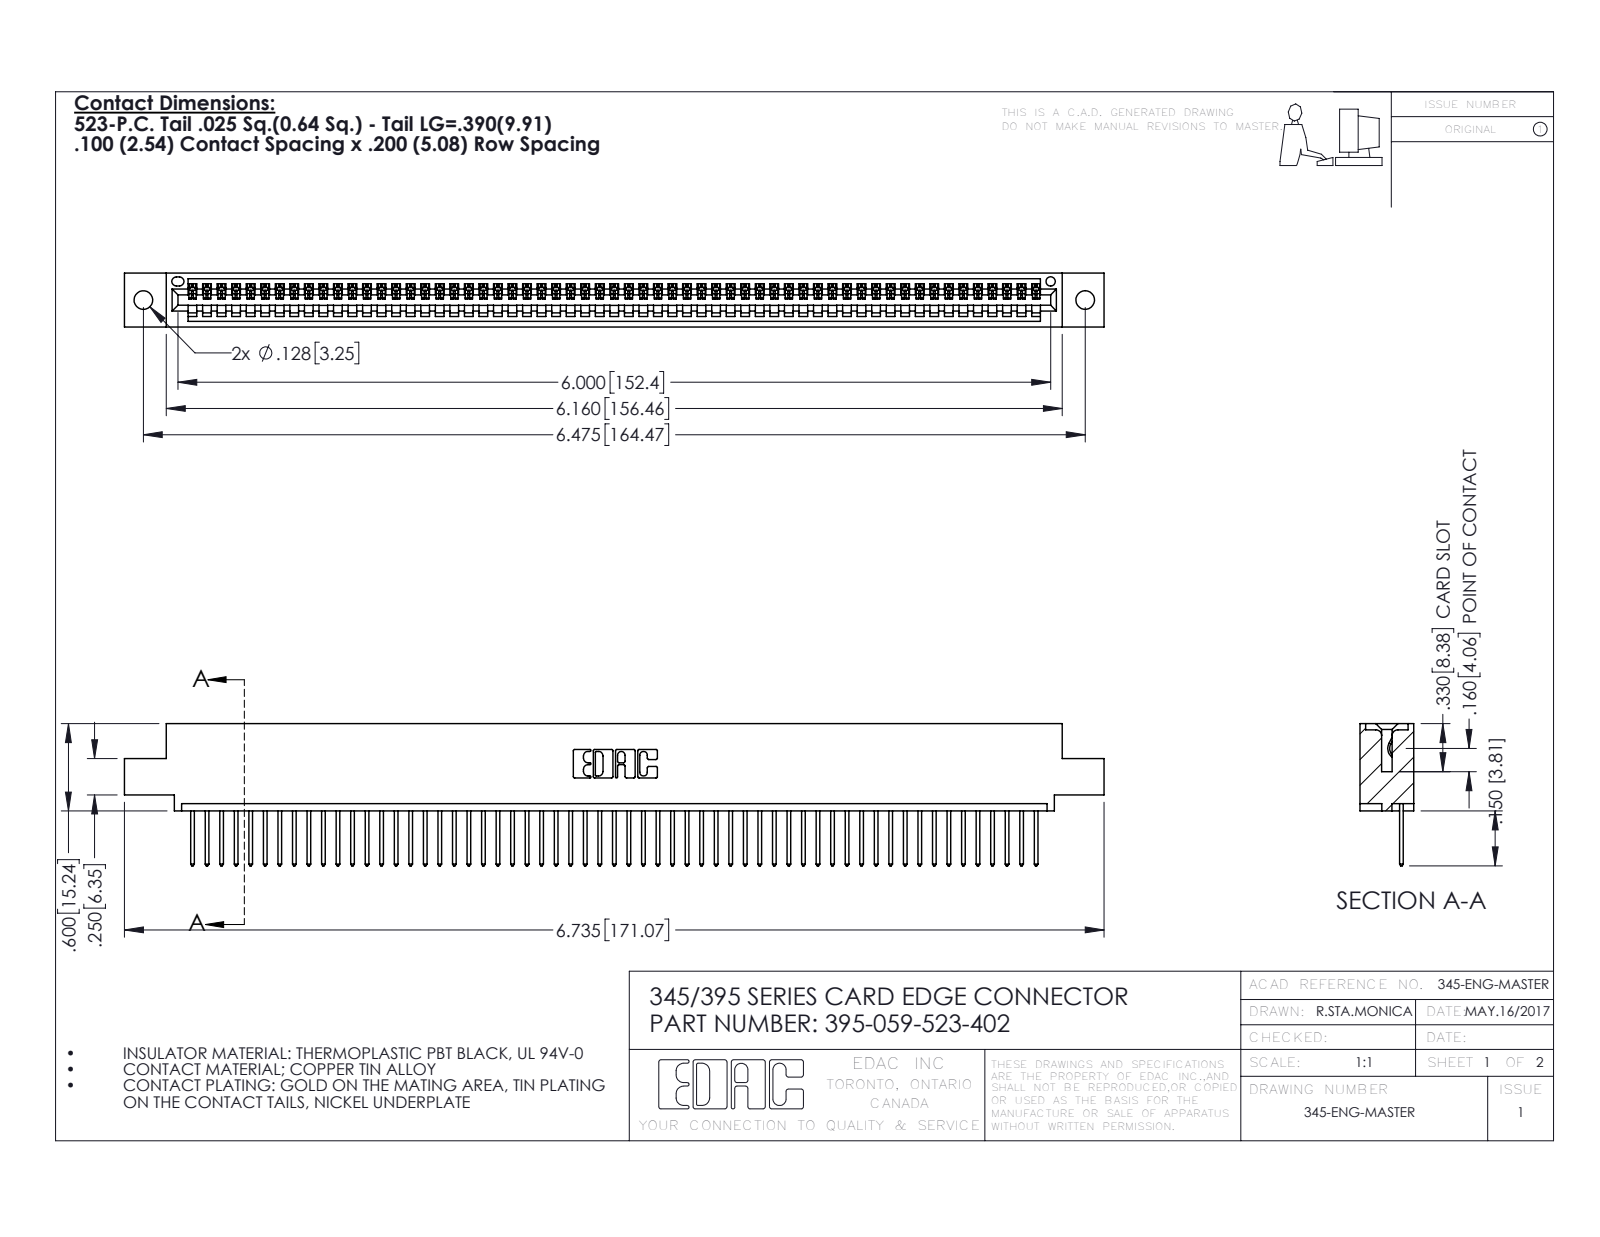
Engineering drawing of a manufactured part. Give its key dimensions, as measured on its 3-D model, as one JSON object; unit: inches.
{"part_name": "345 Part_0.110 Offset - 0.128 Dia; 395-059-523-402; 345-292-001_345-293-123", "step_written_by": "SolidWorks 2016 (CONFIG_CONTROL_DESIGN)", "units": "inches", "bodies": {"solids": 60, "faces": 3552, "planar": 2444, "cylindrical": 1108, "other": 0}, "overall_size": [6.735, 0.977, 0.37], "volume_in3": 0.992, "surface_area_in2": 33.65, "round_holes": [[0.128, 2], [0.064, 1]], "partial_cylinders_radius": [[0.006, 118], [0.01, 118], [0.01, 22], [0.007, 6], [0.031, 6], [0.026, 3], [0.031, 2], [0.04, 2]], "face_to_face_distances": [0.298, 0.072, 0.37, 0.098, 0.272, 0.025, 0.2, 0.225, 0.149, 0.072], "hole_center_spacings": [0.27, 6.239, 6.475]}
